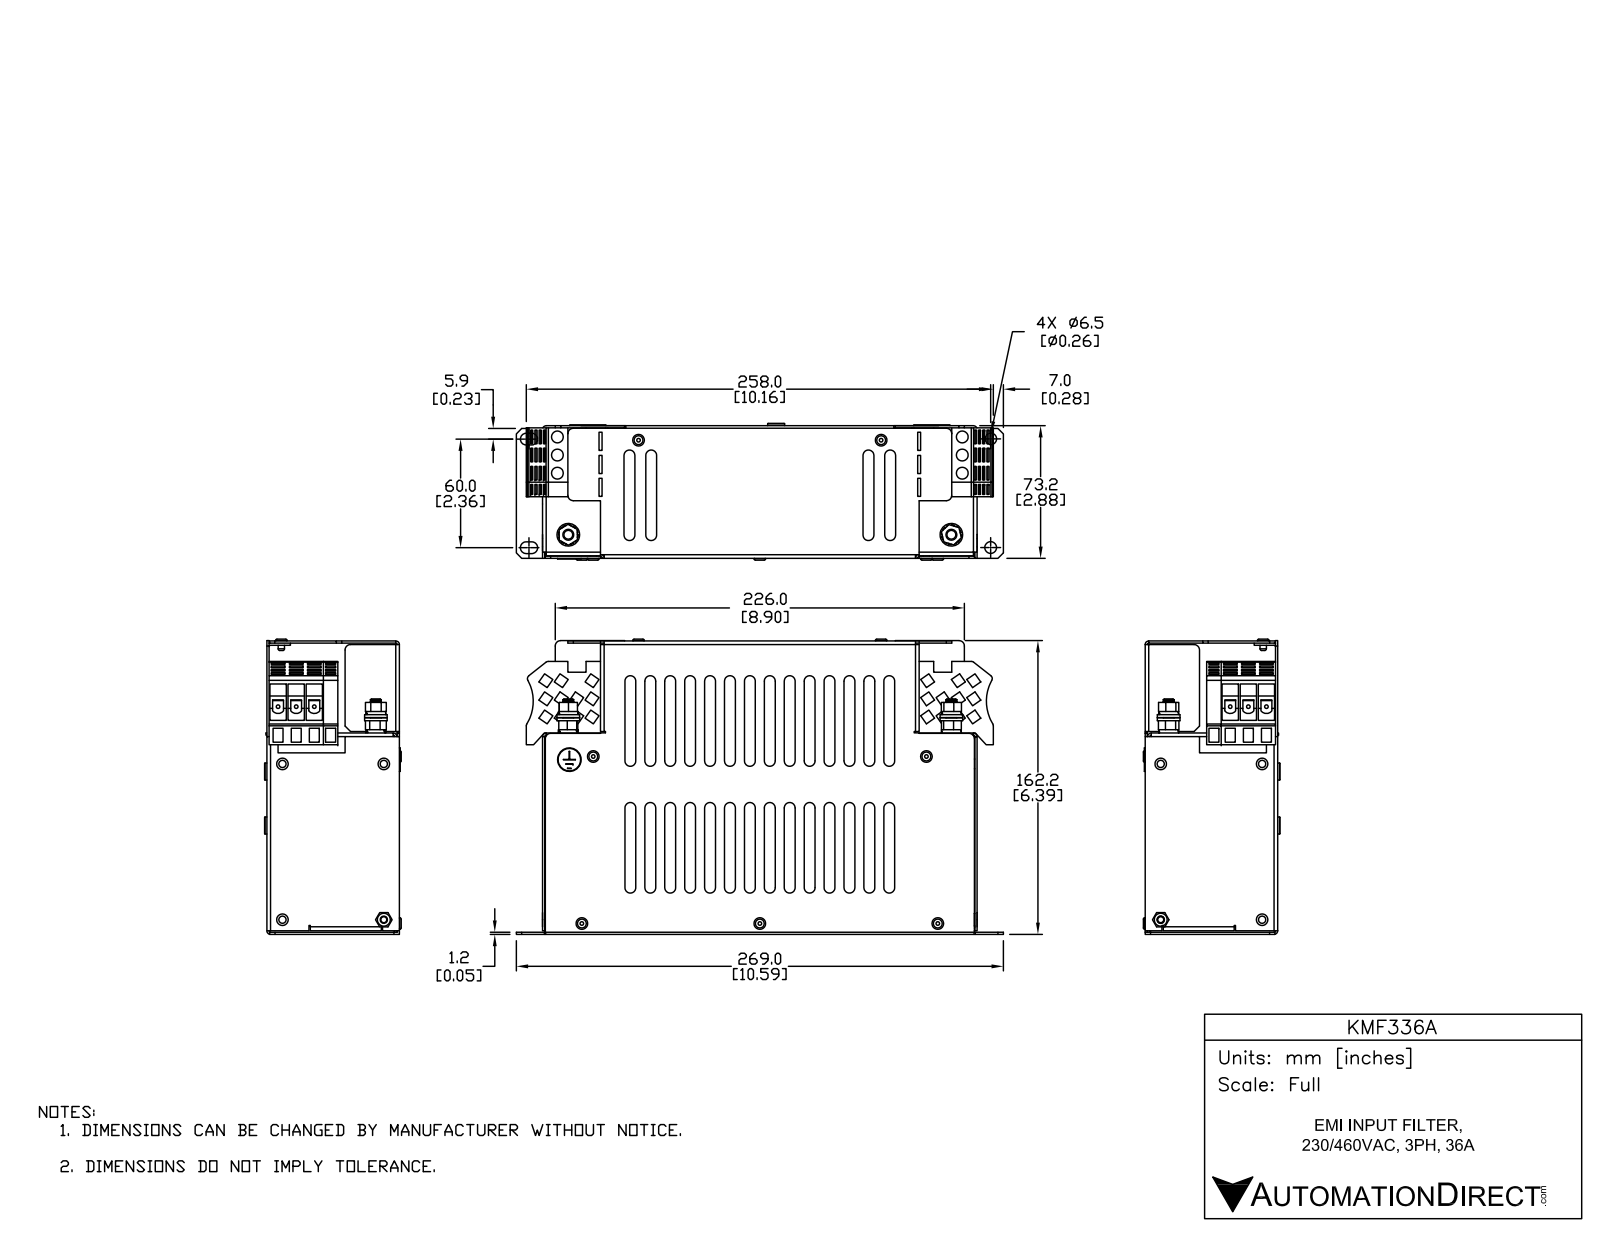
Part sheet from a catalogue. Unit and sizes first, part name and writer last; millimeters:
Units: millimetres
Overall size (bounding box): 272 × 163 × 75.5
Round holes (diameter × count): ⌀6.5 ×16, ⌀3.3 ×12, ⌀3.5 ×11, ⌀6 ×10, ⌀2 ×7, ⌀4 ×4, ⌀4.5 ×2, ⌀5 ×2, ⌀4.8 ×1, ⌀7.1 ×1
Round bosses / shafts (diameter × count): ⌀6.4 ×3, ⌀5.4 ×3, ⌀5.1 ×3, ⌀4.8 ×3, ⌀4.4 ×3, ⌀4.1 ×3, ⌀12.5 ×2, ⌀9.4 ×2
Partial cylindrical surfaces — rounded edges, fillets, slot ends (radius × count): R3 ×75, R2 ×22, R0.8 ×10, R3.3 ×4, R23.9 ×4, R1 ×3, R2.2 ×3, R3.8 ×3
Main face-to-face distances: 1.2, 72, 70.8, 73.2, 160.8, 159.6, 238.8, 162, 110, 50.8
Hole centre spacings: 10, 202.3, 202, 14.7, 14.8, 23.8, 203, 10.7
Volume: 275 500 mm³ · Surface area: 314 600 mm²
Bodies: 37 solids, 3108 faces (1966 planar, 738 cylindrical, 404 other)
Part name (STEP PRODUCT): KMF336A
STEP written by: SolidWorks 2017 (AUTOMOTIVE_DESIGN)
